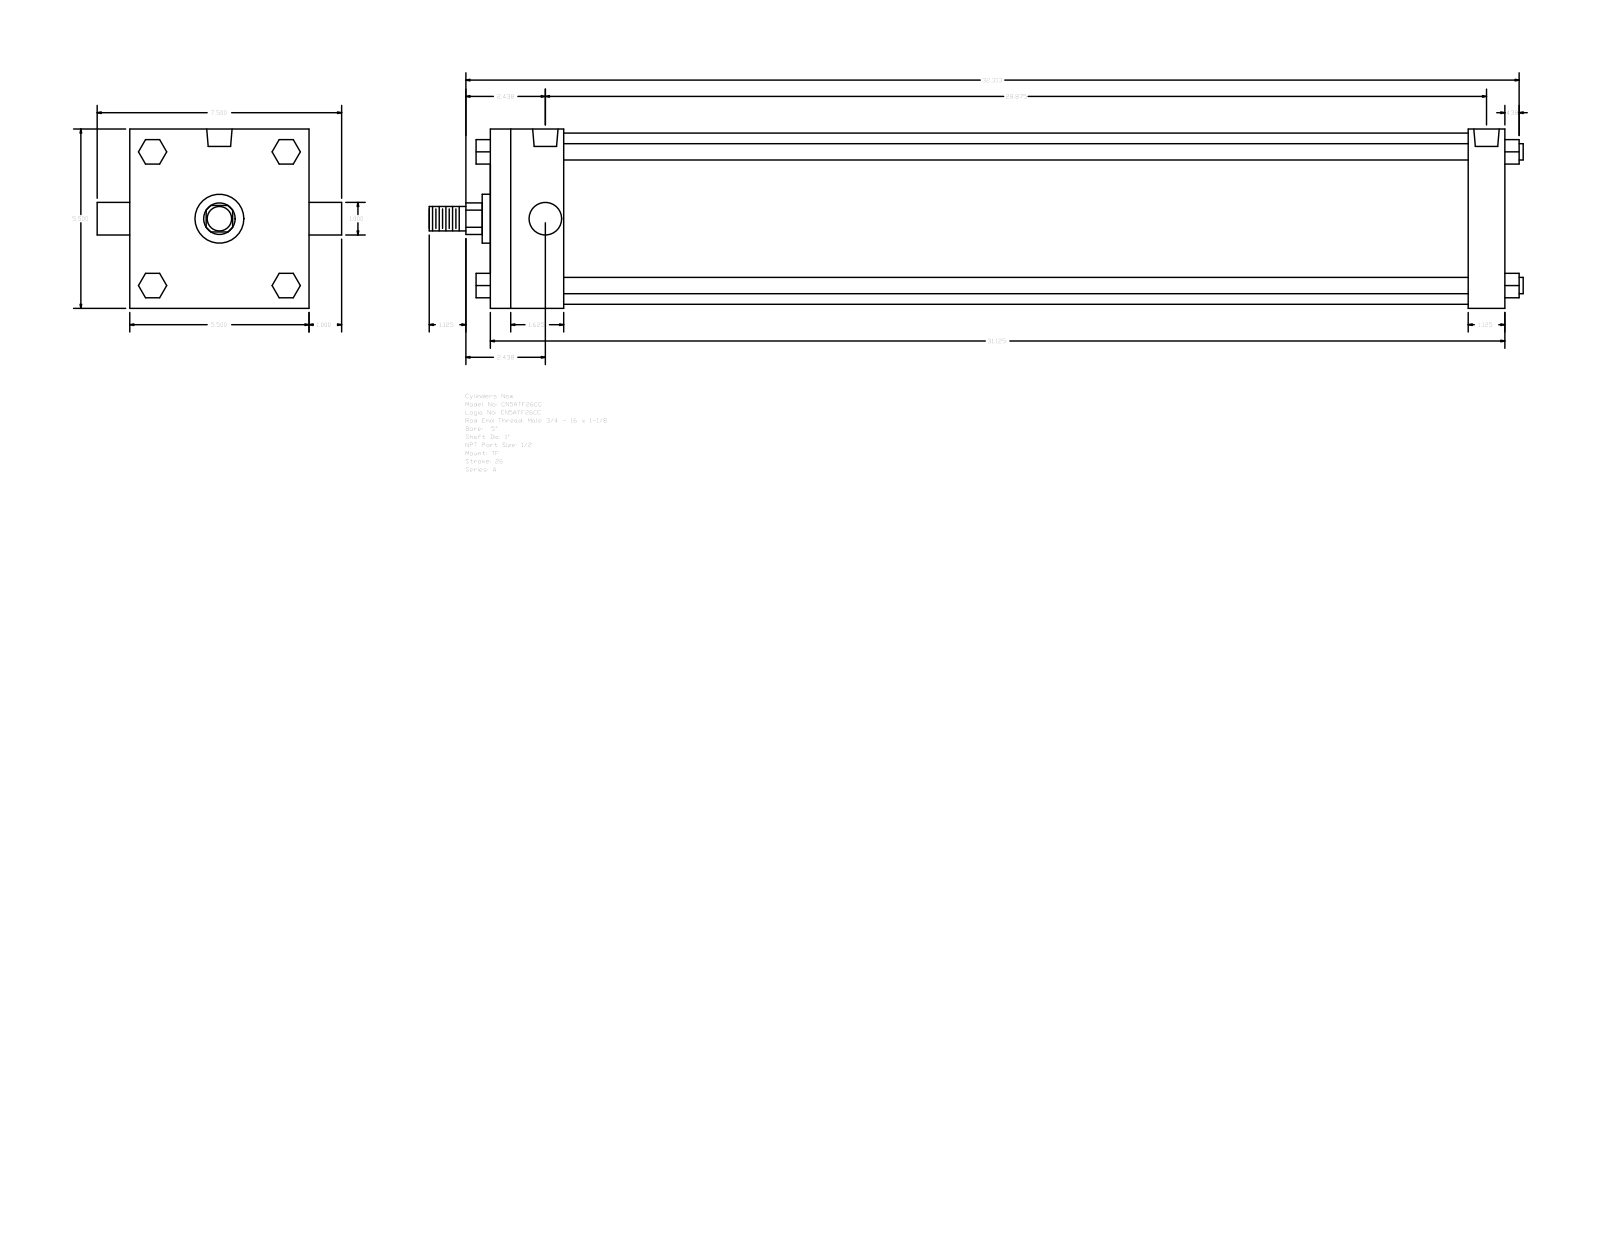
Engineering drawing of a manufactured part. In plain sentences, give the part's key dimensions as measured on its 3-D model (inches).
The part is named "A_TF__0500_1". Its 3-D file was written by "GSSL Pune (CONFIG_CONTROL_DESIGN)". It is 0 solids with 120 faces: 92 planar, 28 cylindrical and 0 other. Overall it measures 33.563 by 7.5 by 5.5 inches. Round holes: 3 of diameter 0.344, 2 of diameter 0.778. Round bosses or shafts: 4 of diameter 0.5, 2 of diameter 1, 1 of diameter 5.25, 1 of diameter 1.5, 1 of diameter 0.75. Partial cylindrical surfaces (rounded edges, fillets, slot ends): 1 of radius 0.484. The main face-to-face distances are 5.5, 31.125, 1.125, 30, 2.25, 27.75, 28.875, 0.75, 2.05, 3.55. The hole center spacings are 0.094, 28.781, 28.687, 28.875.
